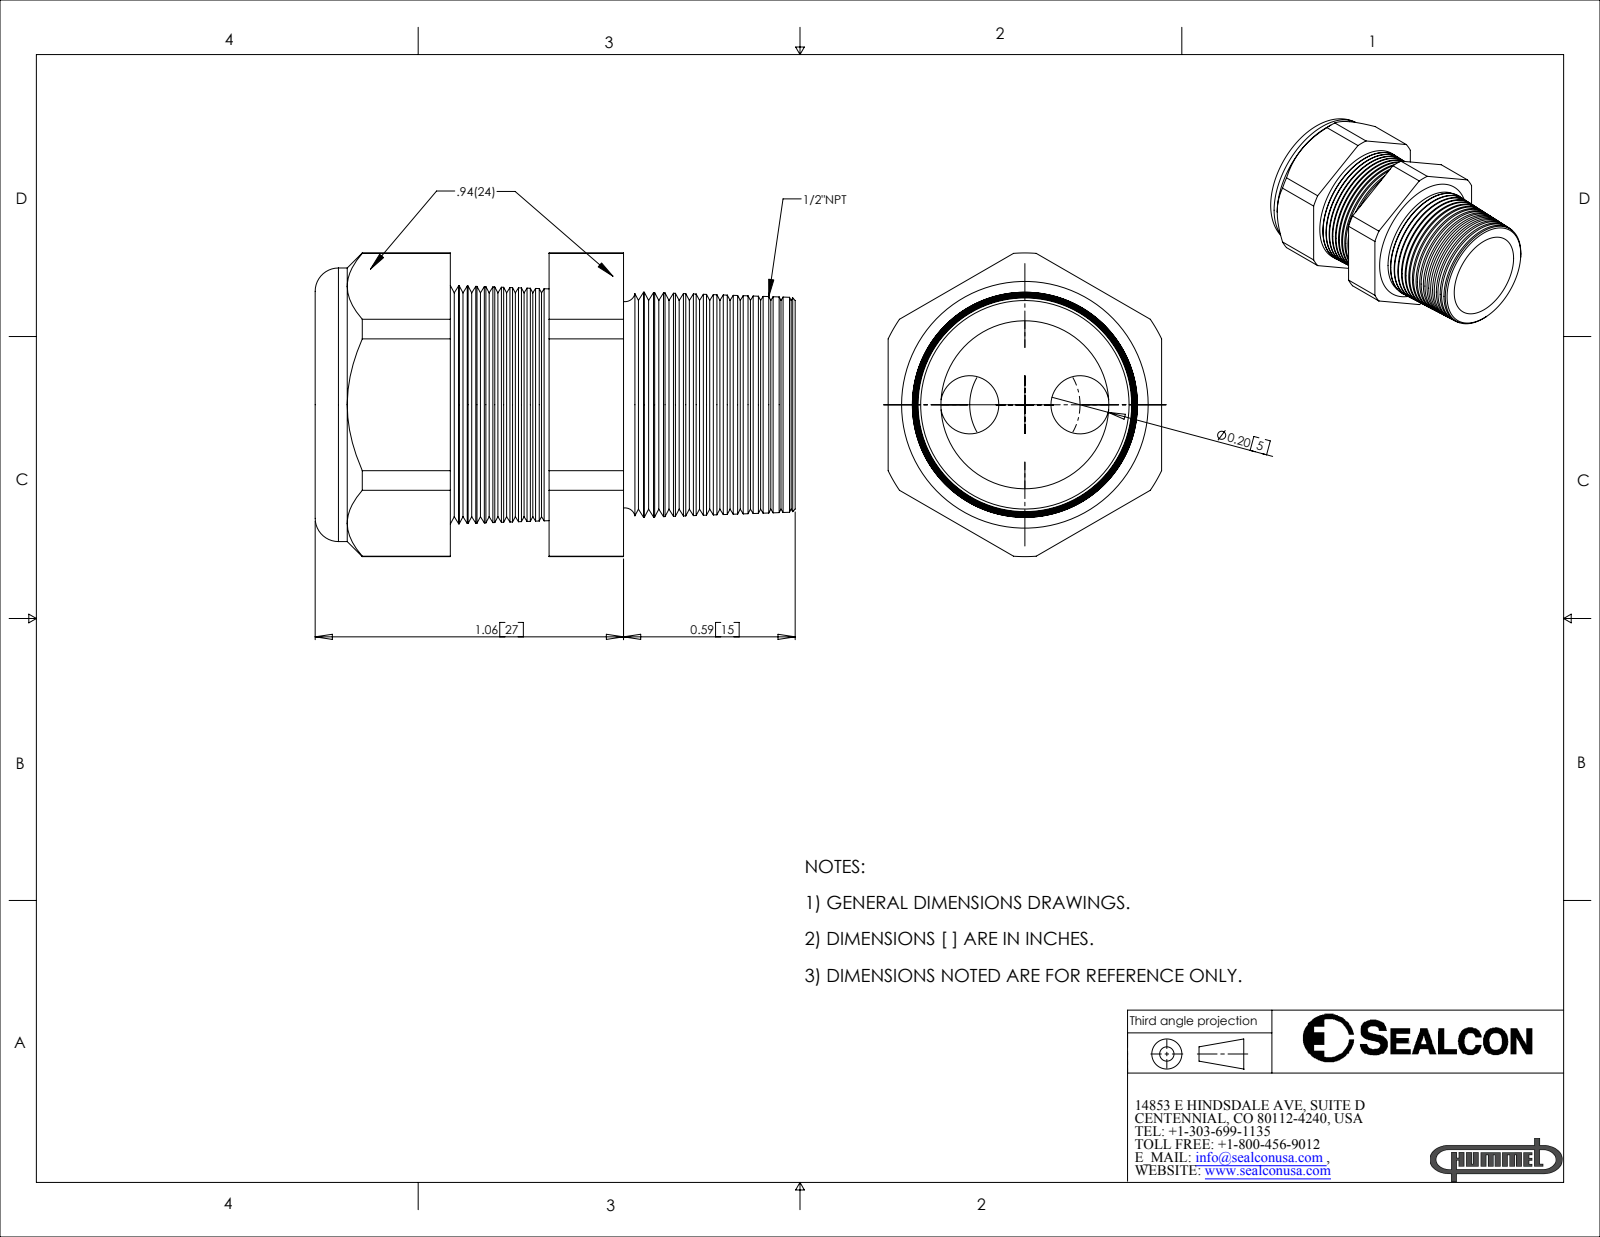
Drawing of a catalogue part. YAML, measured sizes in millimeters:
part_name: "CD13N6-GY"
step_written_by: "SolidWorks 2007 (CONFIG_CONTROL_DESIGN)"
units: millimeters
bodies: {solids: 2, faces: 208, planar: 20, cylindrical: 24, other: 164}
overall_size: [39.9, 26.5, 23.9]
volume: 9140
surface_area: 7490
round_holes:
  - {diameter: 5.1, count: 2}
  - {diameter: 14.7, count: 1}
  - {diameter: 15.2, count: 1}
round_bosses_or_shafts:
  - {diameter: 23.9, count: 1}
partial_cylinders:
  - {radius: 13.3, count: 1}
face_to_face_distances: [23.9, 8.6, 2.9, 11.5, 8.9, 11.8, 20.4, 0.5, 8.4, 11.3]
hole_center_spacings: [4.8, 9.7]
